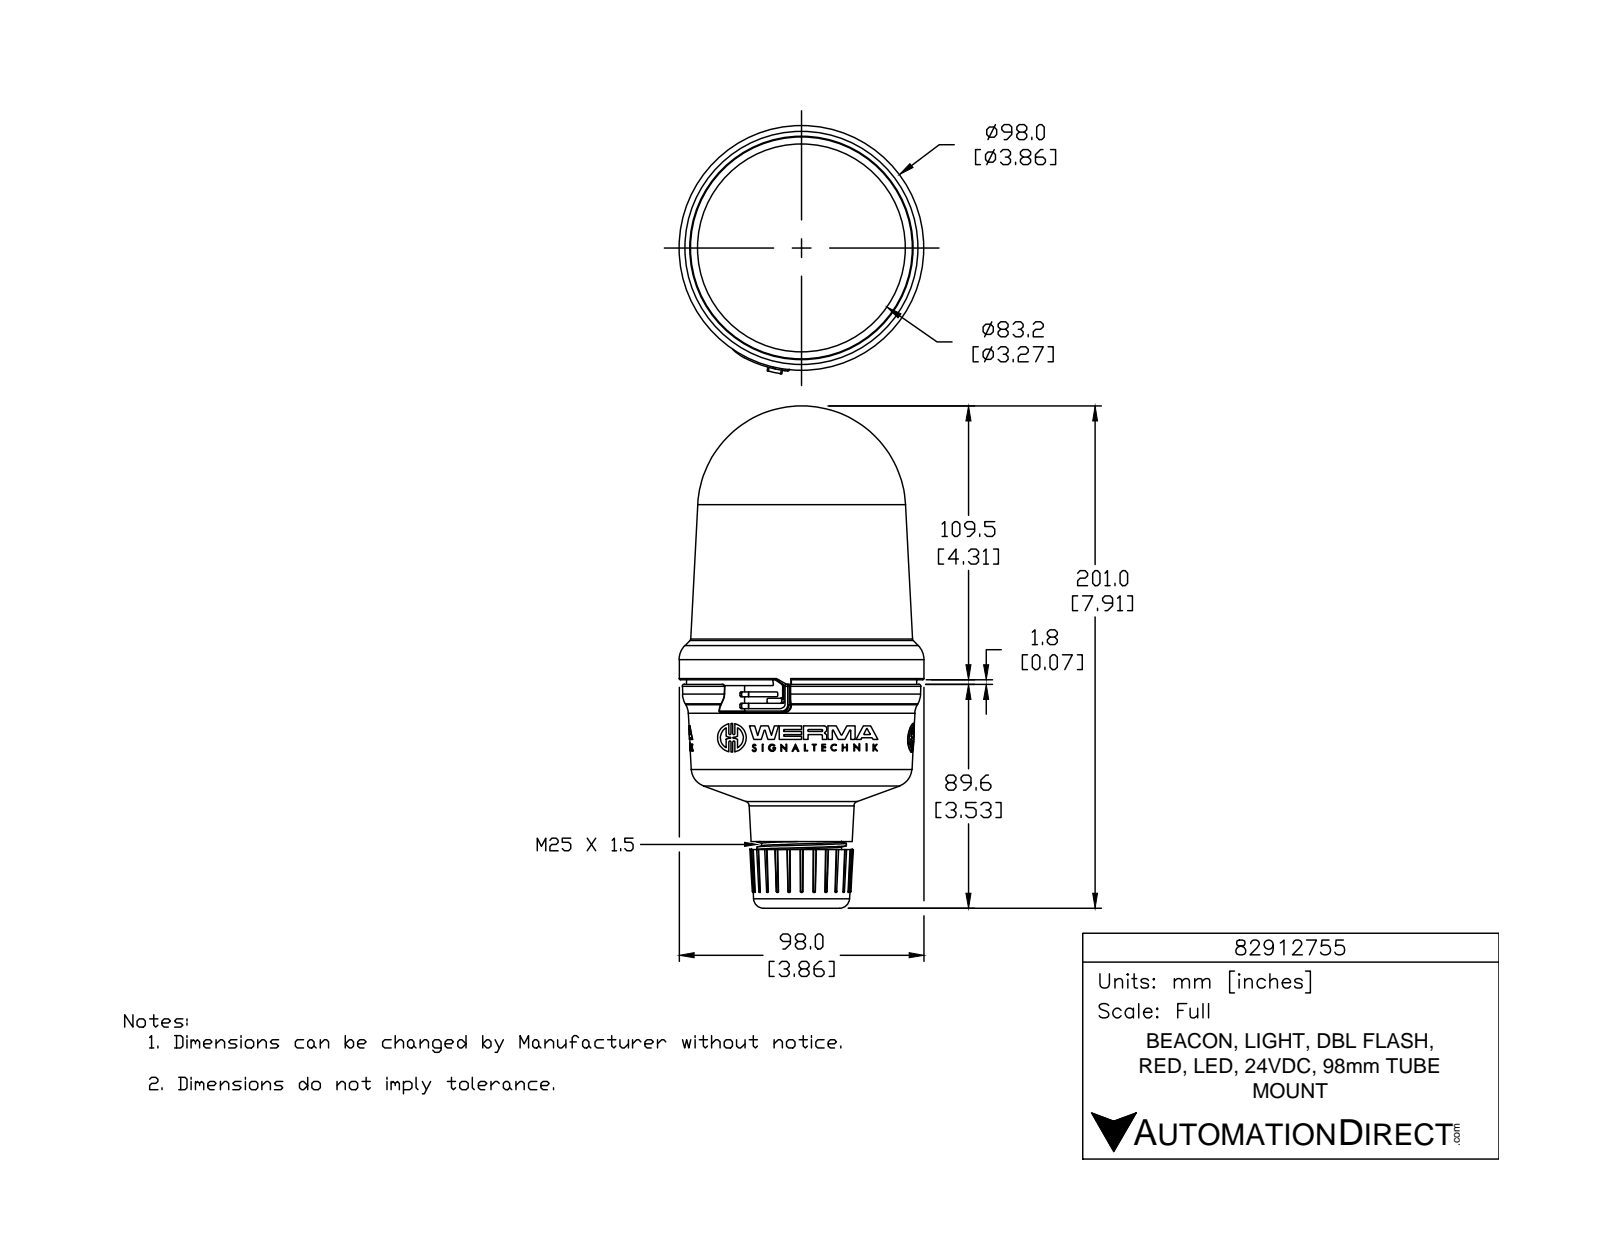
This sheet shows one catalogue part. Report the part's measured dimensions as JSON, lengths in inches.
{"part_name": "82912755", "step_written_by": "SolidWorks 2015 (AUTOMOTIVE_DESIGN)", "units": "inches", "bodies": {"solids": 1, "faces": 1006, "planar": 554, "cylindrical": 189, "other": 263}, "overall_size": [7.914, 3.912, 3.858], "volume_in3": 54.7, "surface_area_in2": 91.39, "round_holes": [[0.078, 3], [1.013, 1], [1.024, 1]], "round_bosses_or_shafts": [[0.452, 3], [0.113, 3], [3.858, 1], [1.409, 1], [1.261, 1]], "partial_cylinders_radius": [[0.02, 12], [0.007, 9], [0.007, 6], [0.016, 6], [0.016, 6], [0.016, 6], [0.262, 6], [0.006, 3]], "face_to_face_distances": [2.214, 0.462, 2.676, 0.335, 0.127, 2.548, 2.603, 2.476, 2.141, 0.073]}
